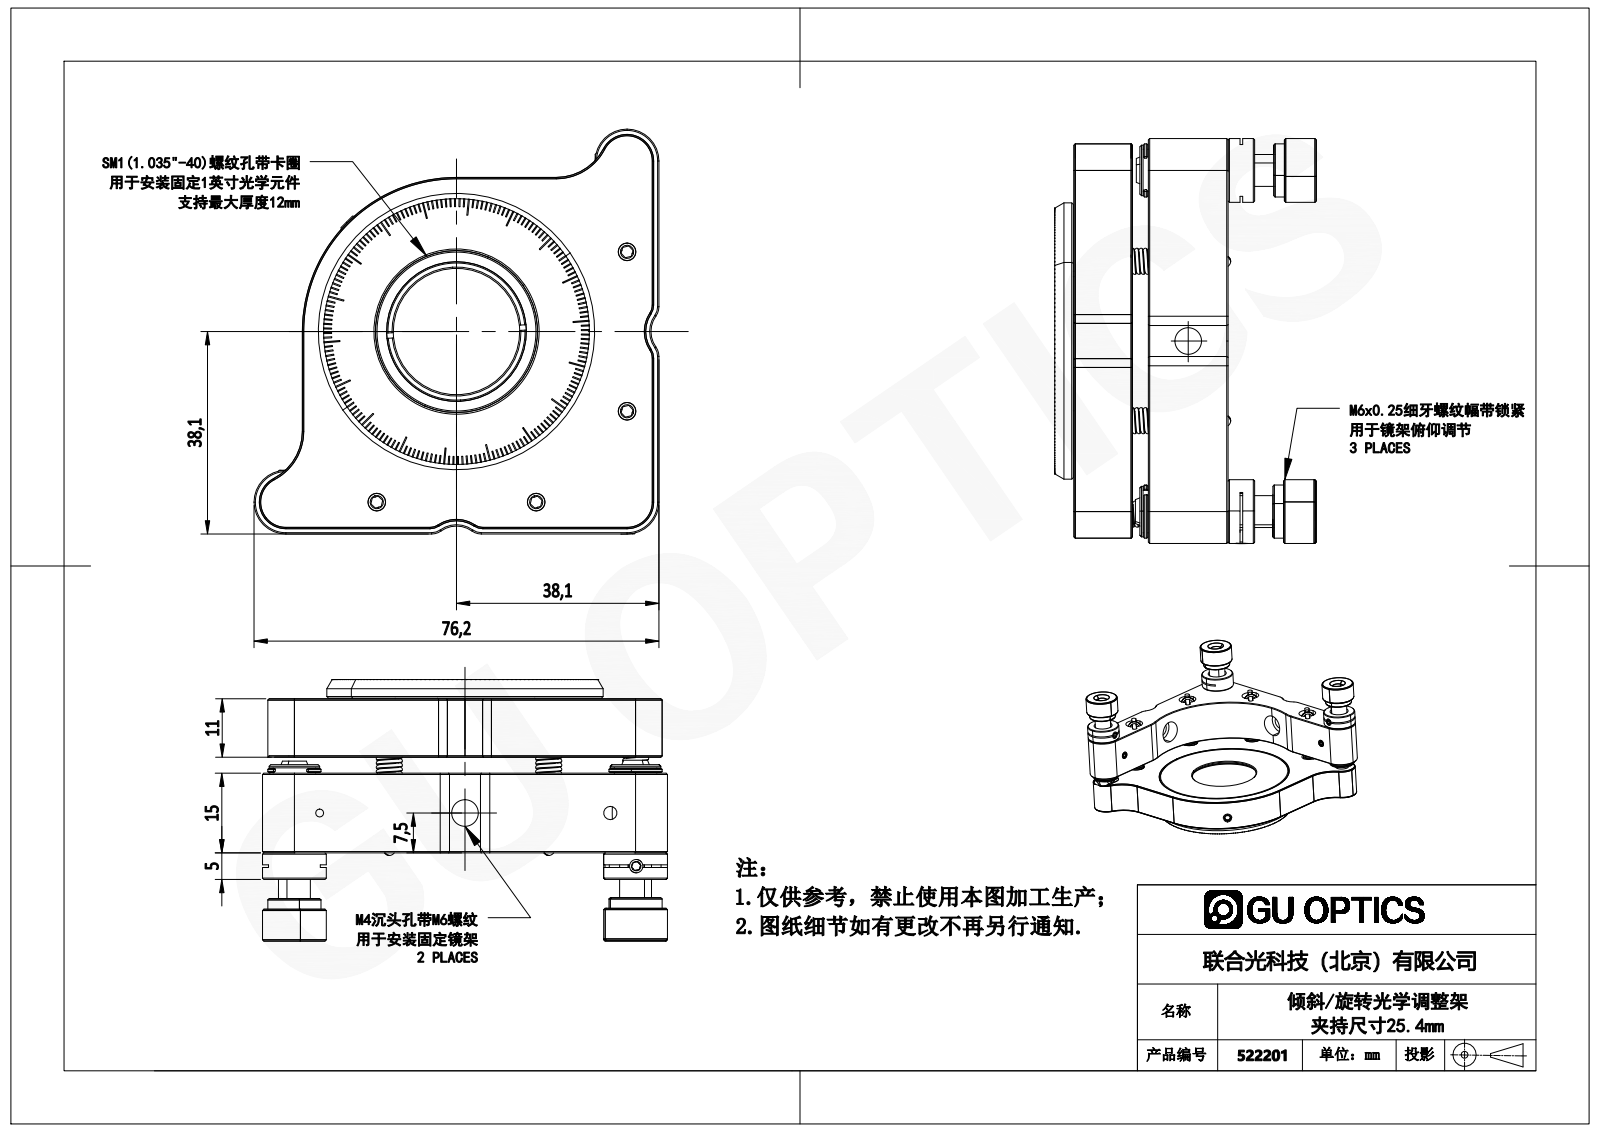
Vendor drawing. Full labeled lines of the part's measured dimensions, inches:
STEP written by: SolidWorks 2020 (CONFIG_CONTROL_DESIGN)
Units: inches
Bodies: 0 solids, 849 faces (460 planar, 0 cylindrical, 389 other)
Overall size (bounding box): 3.001 × 3 × 1.938
Main face-to-face distances: 0.433, 0.575, 0.432, 0.143, 0.576, 1.284, 1.142, 0.709, 0.709, 0.694
